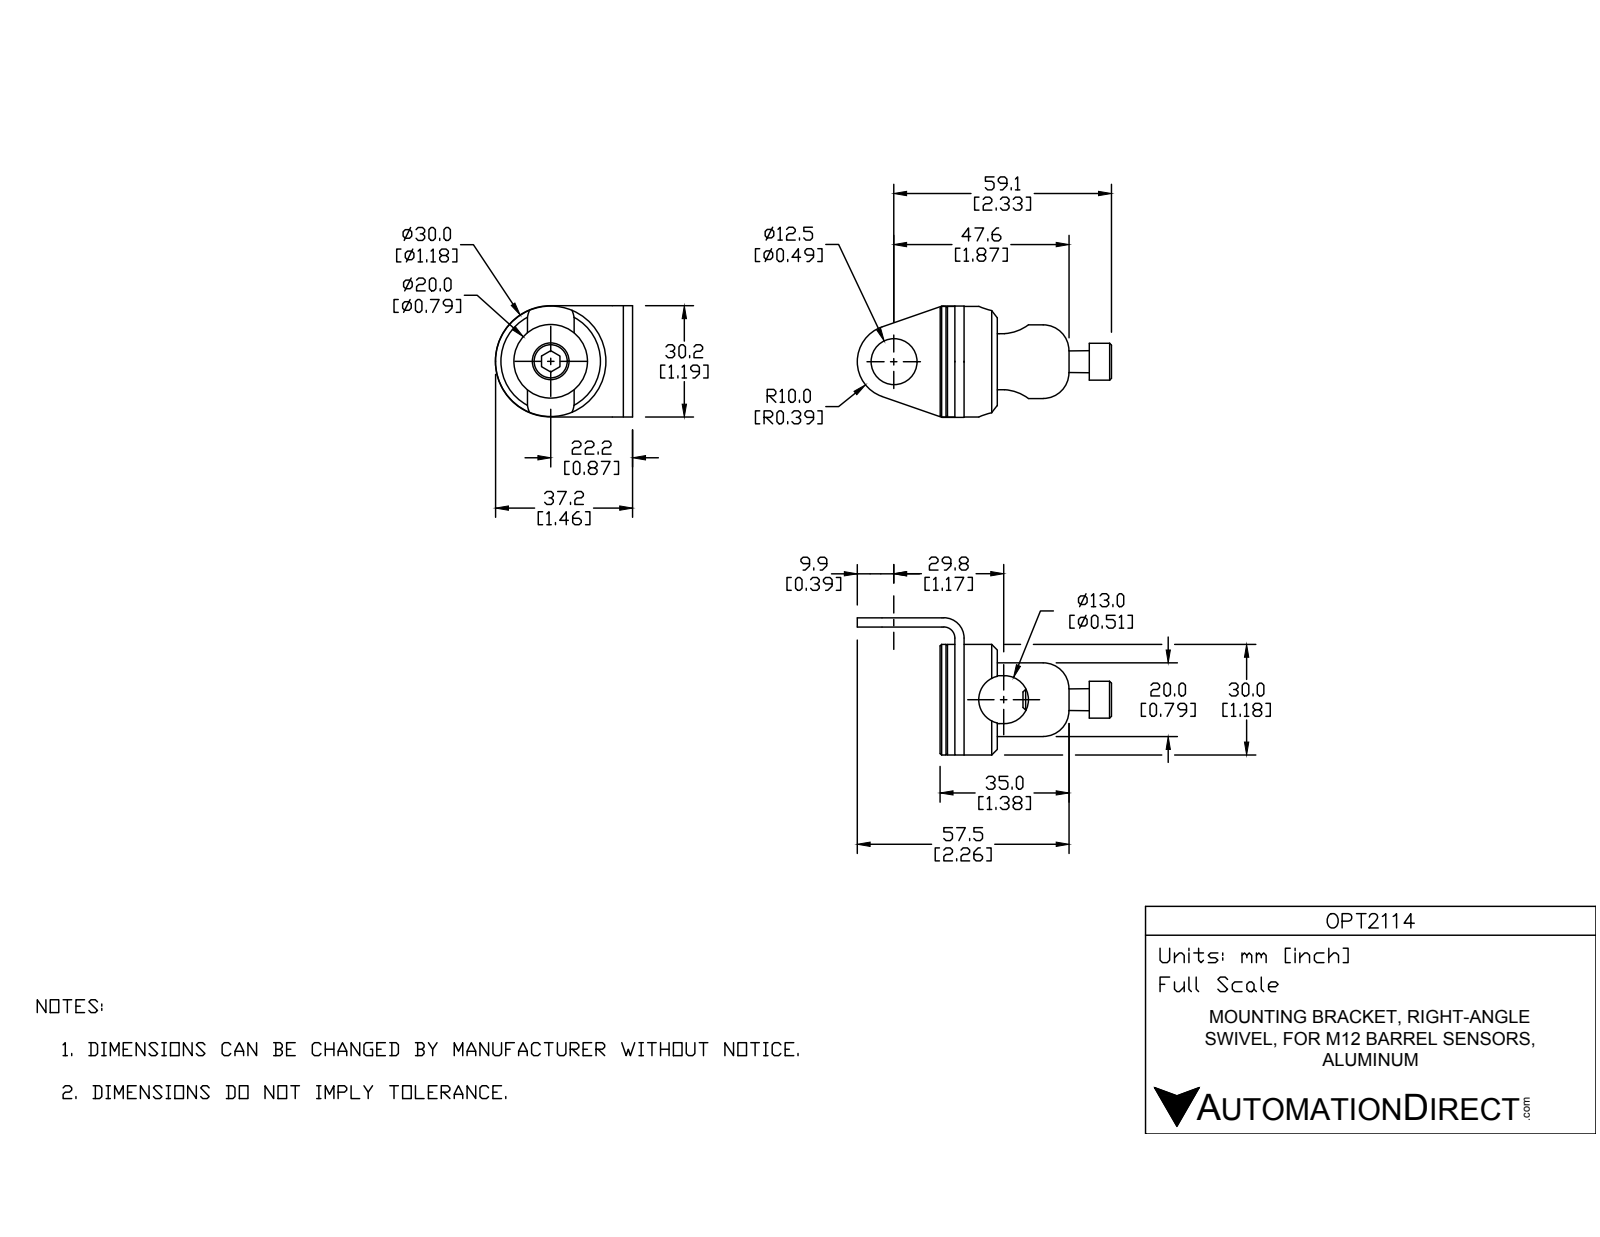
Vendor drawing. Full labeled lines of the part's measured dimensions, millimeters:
STEP written by: Unknown (CONFIG_CONTROL_DESIGN)
Units: millimetres
Bodies: 4 solids, 116 faces (58 planar, 40 cylindrical, 18 other)
Overall size (bounding box): 69 × 52.3 × 45.2
Volume: 30 878 mm³ · Surface area: 17 449 mm²
Round holes (diameter × count): ⌀12.5 ×2, ⌀20.1 ×2, ⌀20 ×1, ⌀21 ×1
Round bosses / shafts (diameter × count): ⌀30 ×1, ⌀10 ×1
Partial cylindrical surfaces — rounded edges, fillets, slot ends (radius × count): R15 ×4, R6.5 ×3, R3 ×2, R5.5 ×2, R10 ×2
Main face-to-face distances: 2.5, 4, 6.5, 1.5, 13, 9, 11.5, 15.5, 2, 0.5
Hole centre spacings: 26.85
